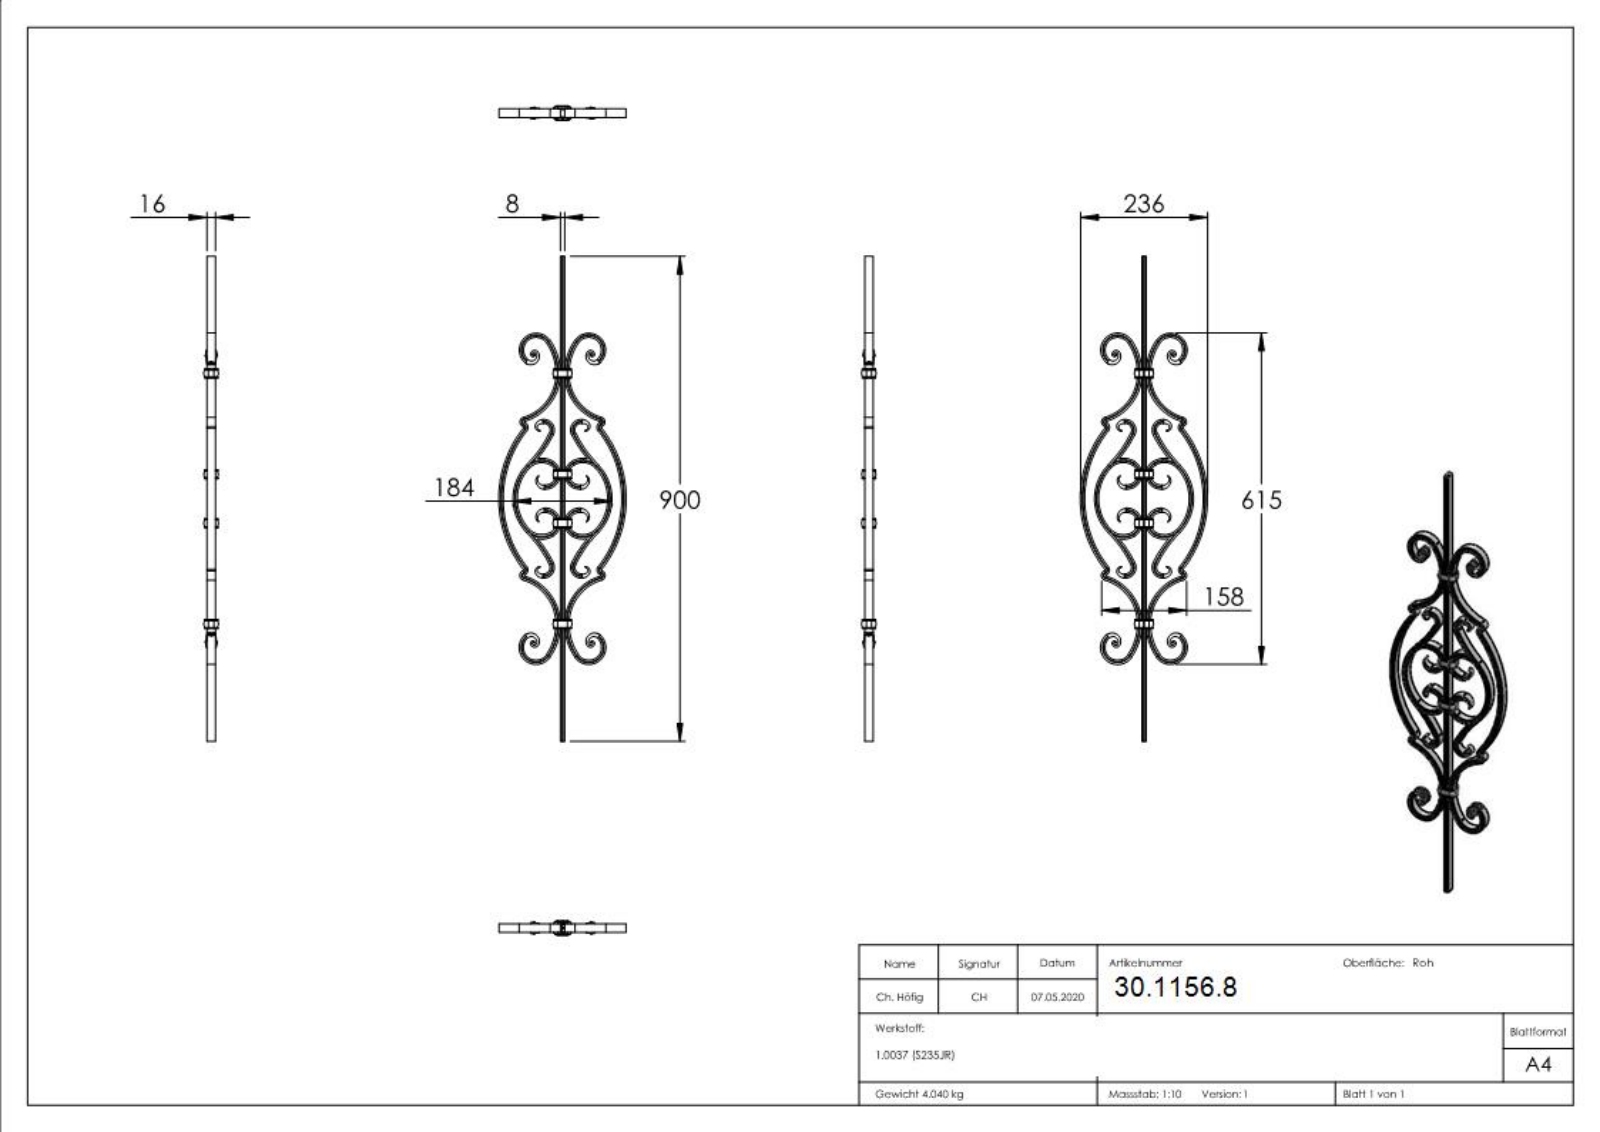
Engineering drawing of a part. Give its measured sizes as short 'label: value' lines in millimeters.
name: 1600 Teil2_1600 Teil2; 1600 Teil3_1600 Teil3; 1600; 1600 Teil4_1600 Teil4 (+1 more)
written by: SolidWorks 2015 (CONFIG_CONTROL_DESIGN)
unit: mm
bodies: 9 solids, 1314 faces (431 planar, 504 cylindrical, 379 other)
size: 900 × 236 × 27
volume: 517 914 mm³; area: 236 435 mm²
rounds: 64× R0.2, 64× R0.5, 20× R1, 20× R10, 4× R2, 4× R3, 4× R4.25, 4× R5.25
face distances: 16, 8, 1.5, 14.5, 13, 3.25, 4.75, 187.14, 277.94, 11.25
